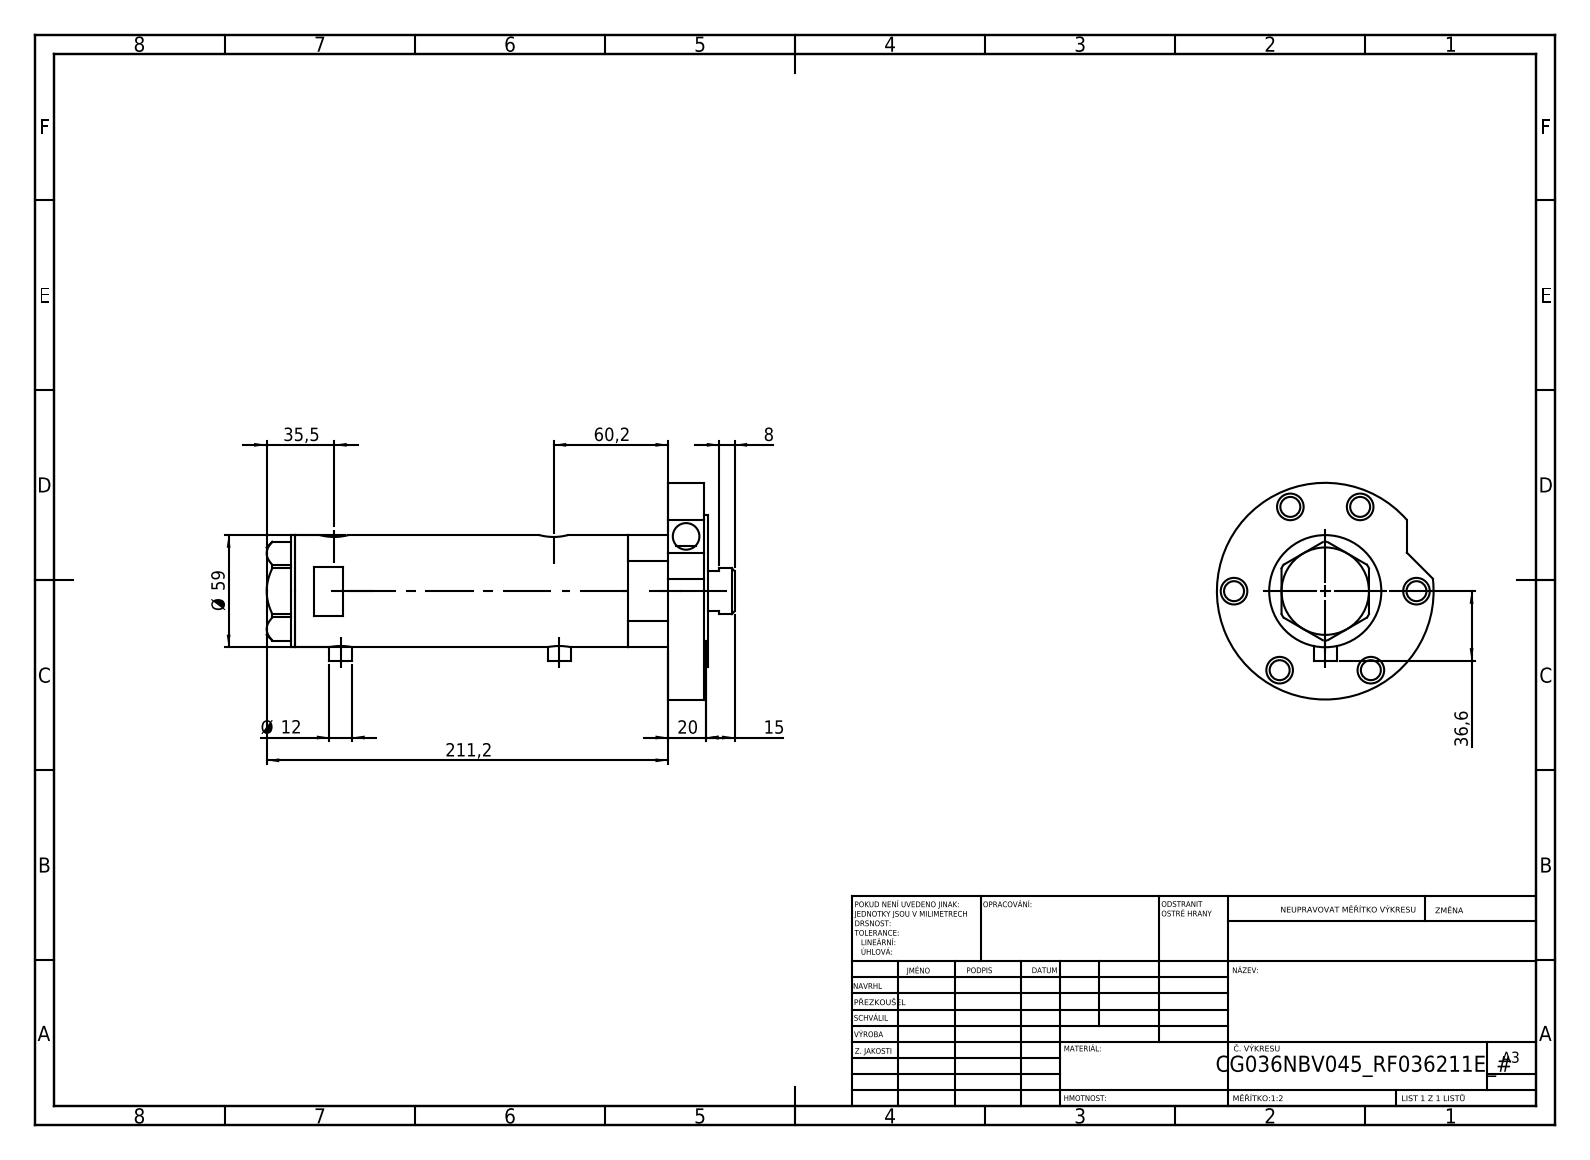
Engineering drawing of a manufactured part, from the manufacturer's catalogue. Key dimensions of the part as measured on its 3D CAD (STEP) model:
Part name (STEP PRODUCT): V270CG_FRONT; V270CG_MIDDLE; V270CG_BACK; V270CG_VC (+1 more)
STEP written by: SolidWorks 2019 (CONFIG_CONTROL_DESIGN)
Units: millimetres
Bodies: 5 solids, 164 faces (62 planar, 82 cylindrical, 20 other)
Overall size (bounding box): 246.2 × 114 × 114
Volume: 712 950 mm³ · Surface area: 148 023 mm²
Round holes (diameter × count): ⌀14 ×7, ⌀10.5 ×6, ⌀9.73 ×2, ⌀12.5 ×2, ⌀15 ×2, ⌀8.5 ×1, ⌀25 ×1, ⌀26.5 ×1, ⌀36 ×1, ⌀40 ×1, ⌀48 ×1, ⌀52 ×1
Round bosses / shafts (diameter × count): ⌀12 ×2, ⌀114 ×1, ⌀80 ×1, ⌀59 ×1, ⌀46 ×1, ⌀24 ×1
Main face-to-face distances: 2, 19, 21, 217.2, 196.2, 215.2, 137.2, 59, 78, 80
Hole centre spacings: 48, 53.34, 79.82, 83.14, 86.1, 95.8, 2.9, 3.5
